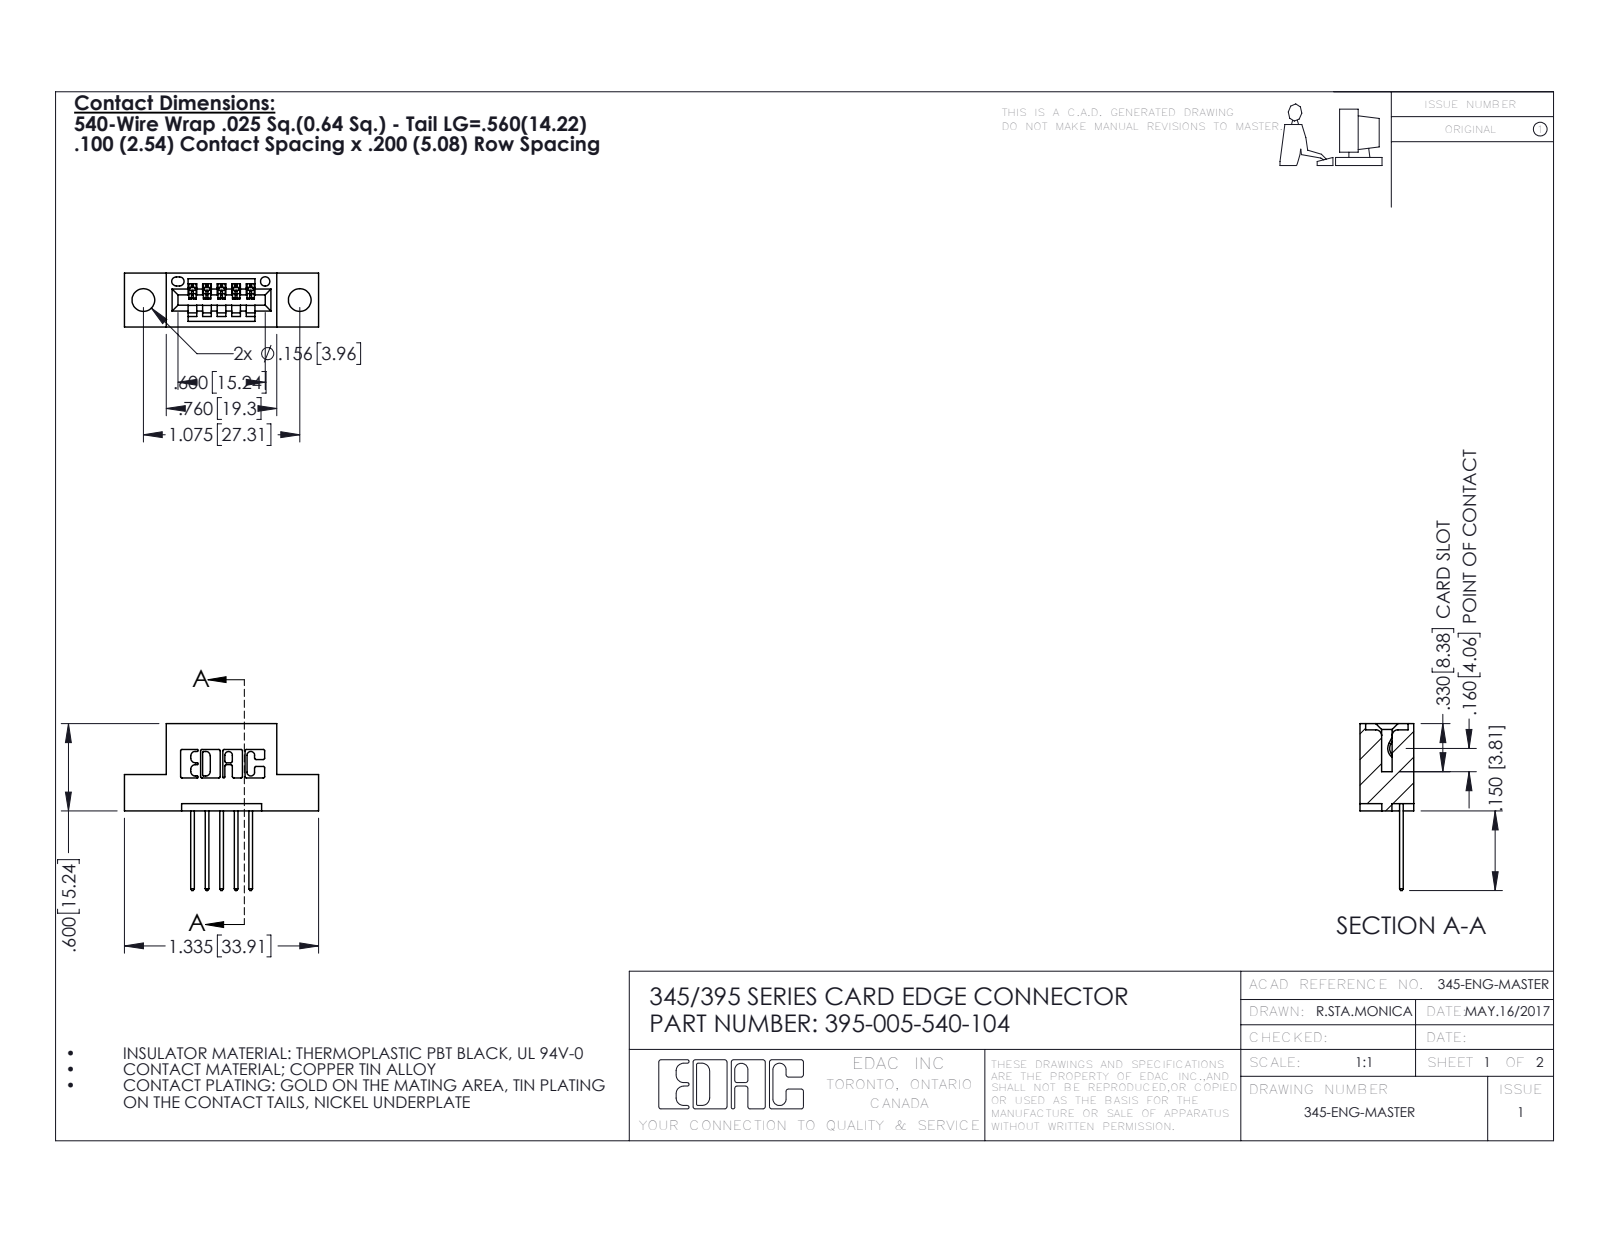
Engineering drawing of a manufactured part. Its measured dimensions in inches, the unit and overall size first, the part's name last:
Units: inches
Overall size (bounding box): 1.335 × 1.147 × 0.37
Round holes (diameter × count): ⌀0.156 ×2, ⌀0.064 ×1
Partial cylindrical surfaces — rounded edges, fillets, slot ends (radius × count): R0.01 ×22, R0.006 ×10, R0.01 ×10, R0.007 ×6, R0.031 ×6, R0.026 ×3, R0.031 ×2, R0.04 ×2
Main face-to-face distances: 0.2, 0.37, 0.298, 0.072, 0.1, 0.025, 0.098, 0.272, 0.25, 0.06
Hole centre spacings: 0.27, 0.847, 1.075
Volume: 0.173 in³ · Surface area: 4.842 in²
Bodies: 6 solids, 416 faces (280 planar, 136 cylindrical, 0 other)
Part name (STEP PRODUCT): 345 Part_Flush Mounting Lugs - 0.156 Dia-TH; 395-005-540-104; 345-292-001_345-293-140
STEP written by: SolidWorks 2016 (CONFIG_CONTROL_DESIGN)
